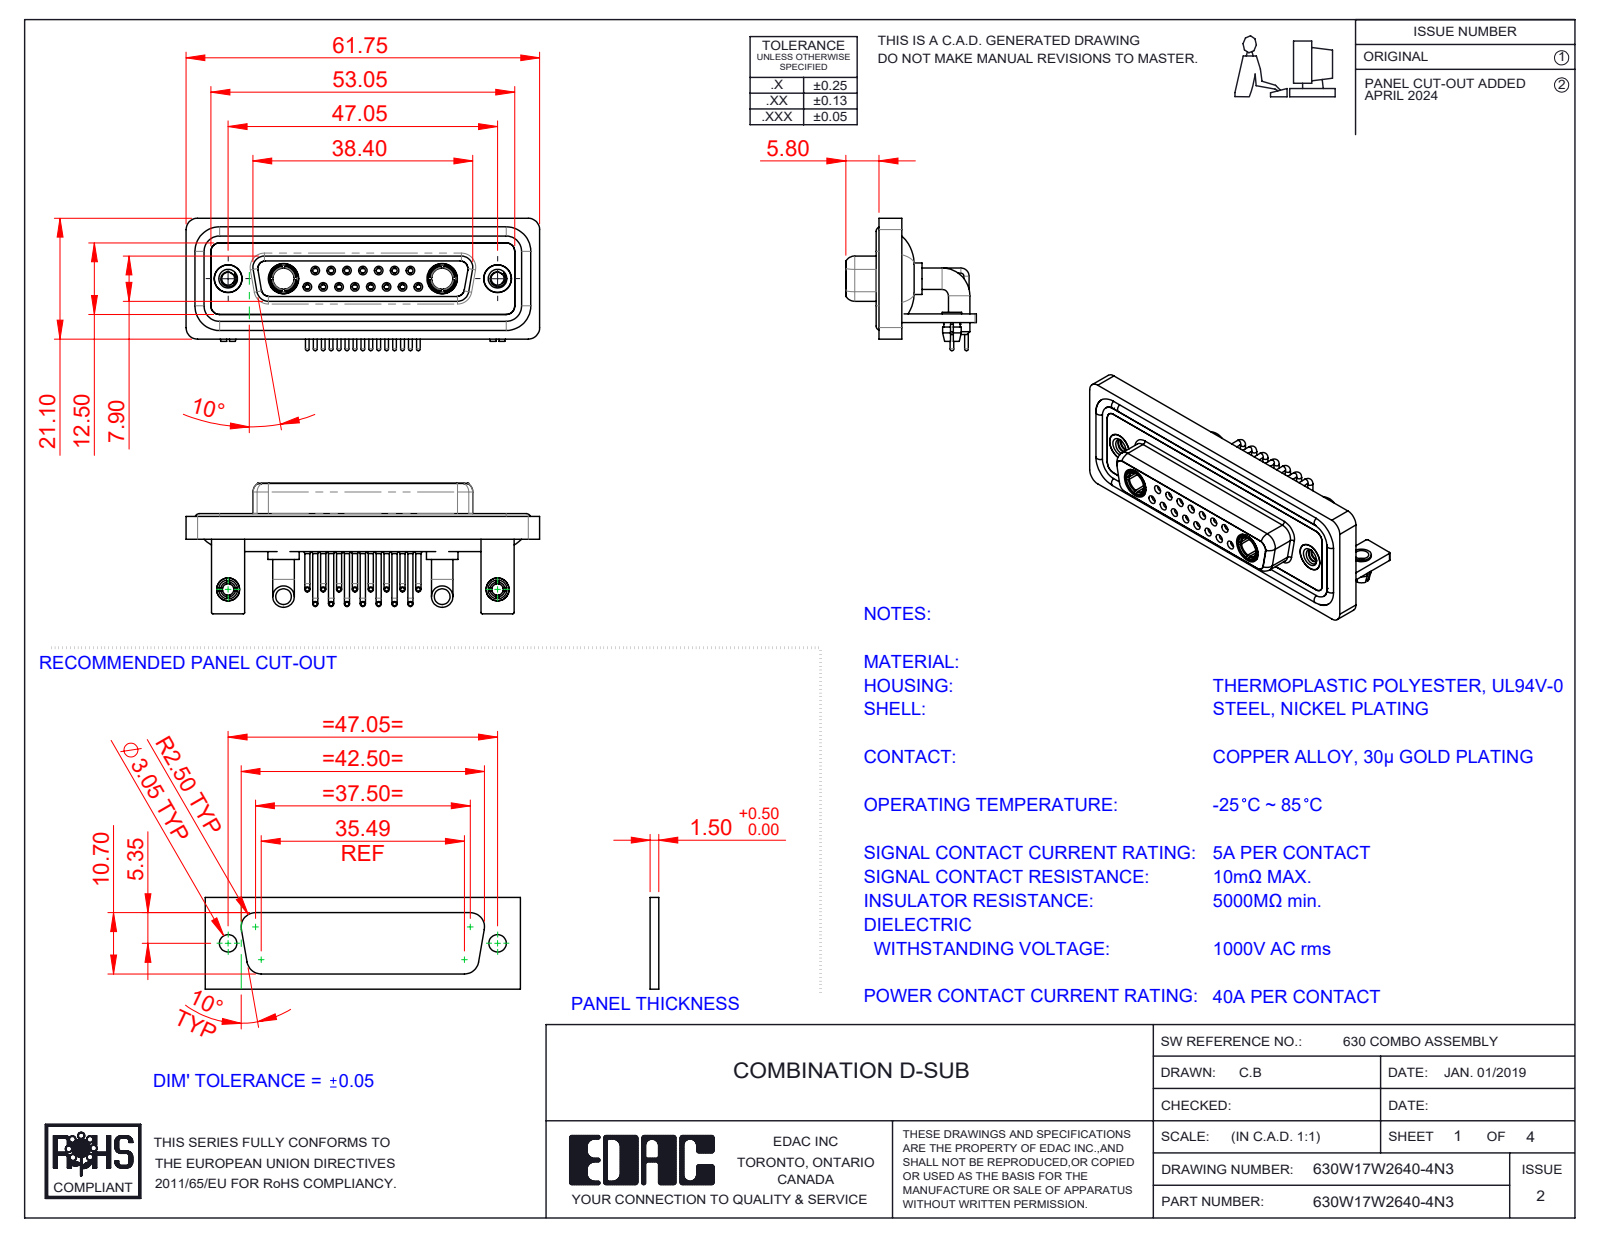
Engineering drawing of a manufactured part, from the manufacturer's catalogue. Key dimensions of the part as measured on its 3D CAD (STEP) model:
Part name (STEP PRODUCT): 630Combo Contact Row 2_50 Contacts; 630Combo Housing_17W2; 630W17W2640-4N3; 630Combo Shell Front_25 Contacts (+7 more)
STEP written by: SolidWorks 2023 (CONFIG_CONTROL_DESIGN)
Units: millimetres
Bodies: 30 solids, 1477 faces (456 planar, 639 cylindrical, 382 other)
Overall size (bounding box): 61.75 × 23.12 × 22.8
Volume: 9 035 mm³ · Surface area: 15 564 mm²
Round holes (diameter × count): ⌀2 ×17, ⌀0.9 ×15, ⌀1.1 ×15, ⌀1.5 ×15, ⌀1.6 ×8, ⌀1.7 ×7, ⌀4.85 ×4, ⌀2.26 ×2, ⌀2.5 ×2, ⌀3.2 ×2, ⌀3.7 ×2, ⌀4 ×2
Round bosses / shafts (diameter × count): ⌀0.9 ×15, ⌀0.65 ×15, ⌀1.6 ×11, ⌀3.75 ×4, ⌀5.5 ×2, ⌀5.2 ×2, ⌀4.96 ×2, ⌀4.95 ×2
Partial cylindrical surfaces — rounded edges, fillets, slot ends (radius × count): R2 ×19, R1.5 ×18, R0.25 ×16, R1.35 ×8, R1.6 ×8, R0.5 ×5, R0.6 ×4, R0.65 ×4
Main face-to-face distances: 0.4, 1.8, 2.9, 3.7, 1.5, 4.1, 1.1, 1.4, 1.6, 3.1
Hole centre spacings: 3.16, 2.77, 5.54, 8.31, 5.04, 7.49, 11.08, 5.03
